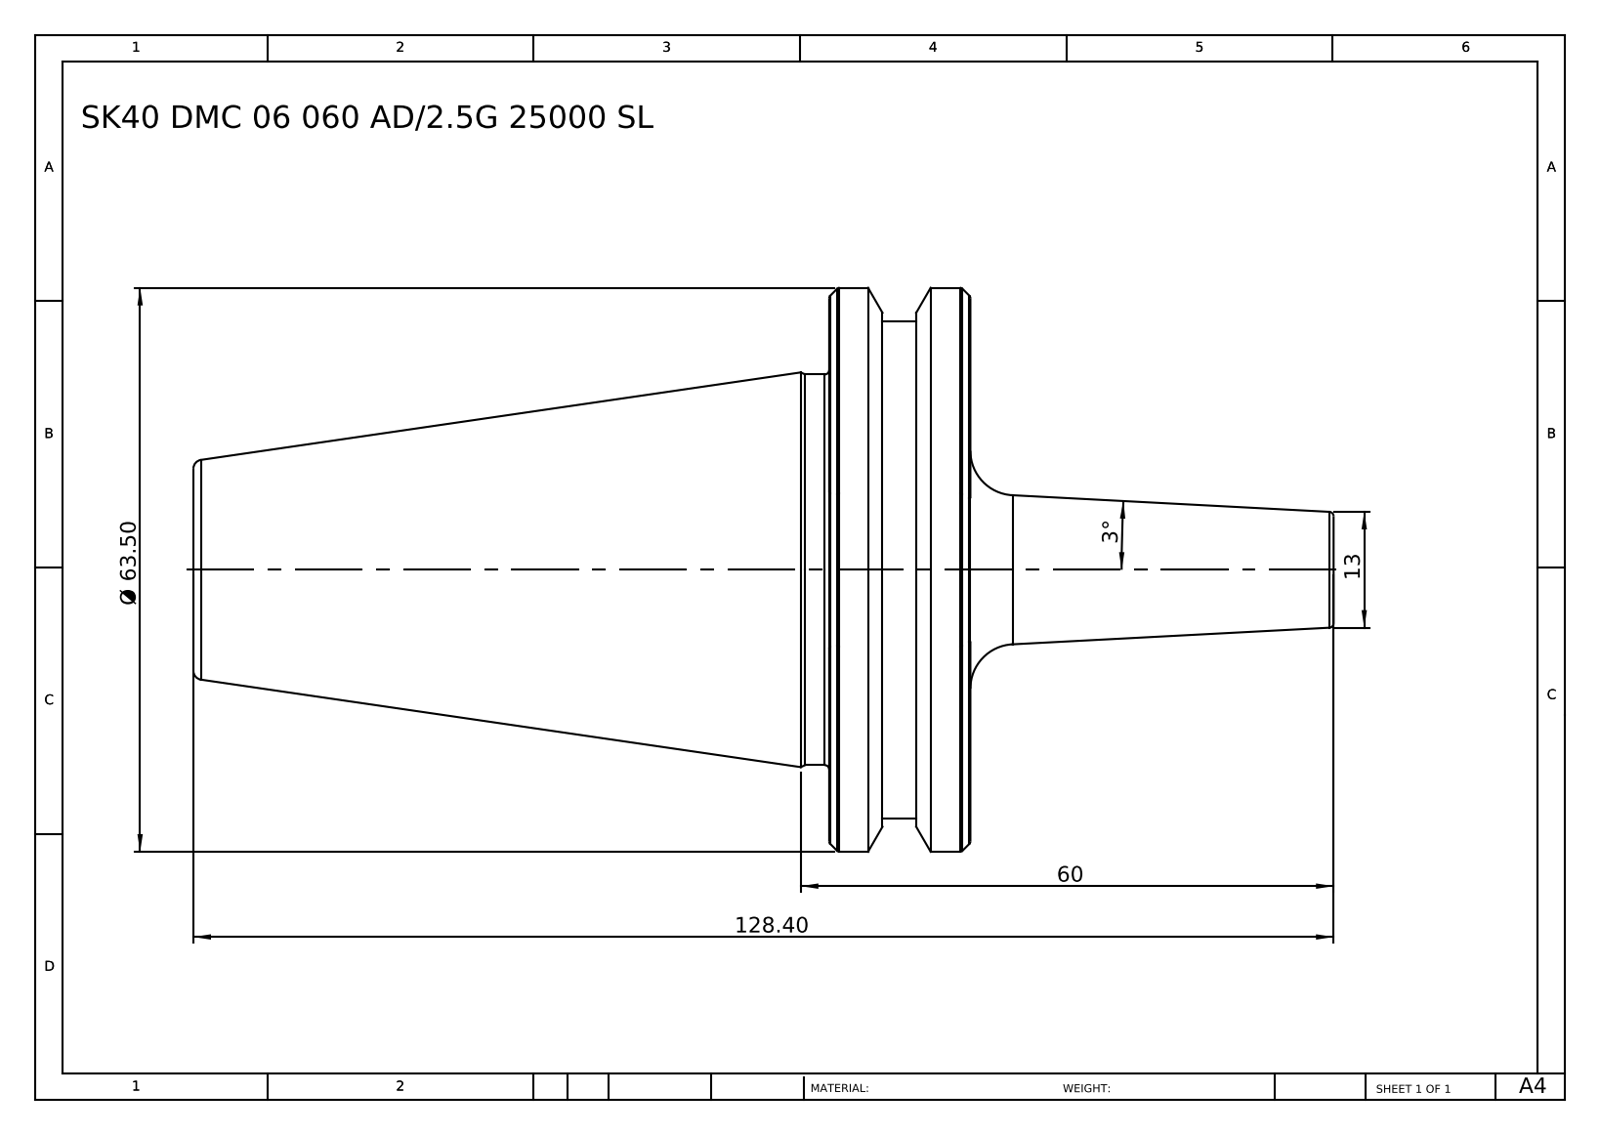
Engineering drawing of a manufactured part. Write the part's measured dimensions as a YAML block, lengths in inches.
part_name: "SK 40 DMC 06 060 AD-2.5G 25000 SL"
step_written_by: "SolidWorks 2014 (CONFIG_CONTROL_DESIGN)"
units: inches
bodies: {solids: 1, faces: 64, planar: 6, cylindrical: 8, other: 50}
overall_size: [5.055, 2.5, 2.5]
volume: 7.616
surface_area: 28.94
round_bosses_or_shafts:
  - {diameter: 2.5, count: 1}
  - {diameter: 2.205, count: 1}
  - {diameter: 1.732, count: 1}
face_to_face_distances: [0.626, 3.445, 2.819, 0.24, 0.386, 3.205, 0.39, 0.15, 0.236, 3.055]
